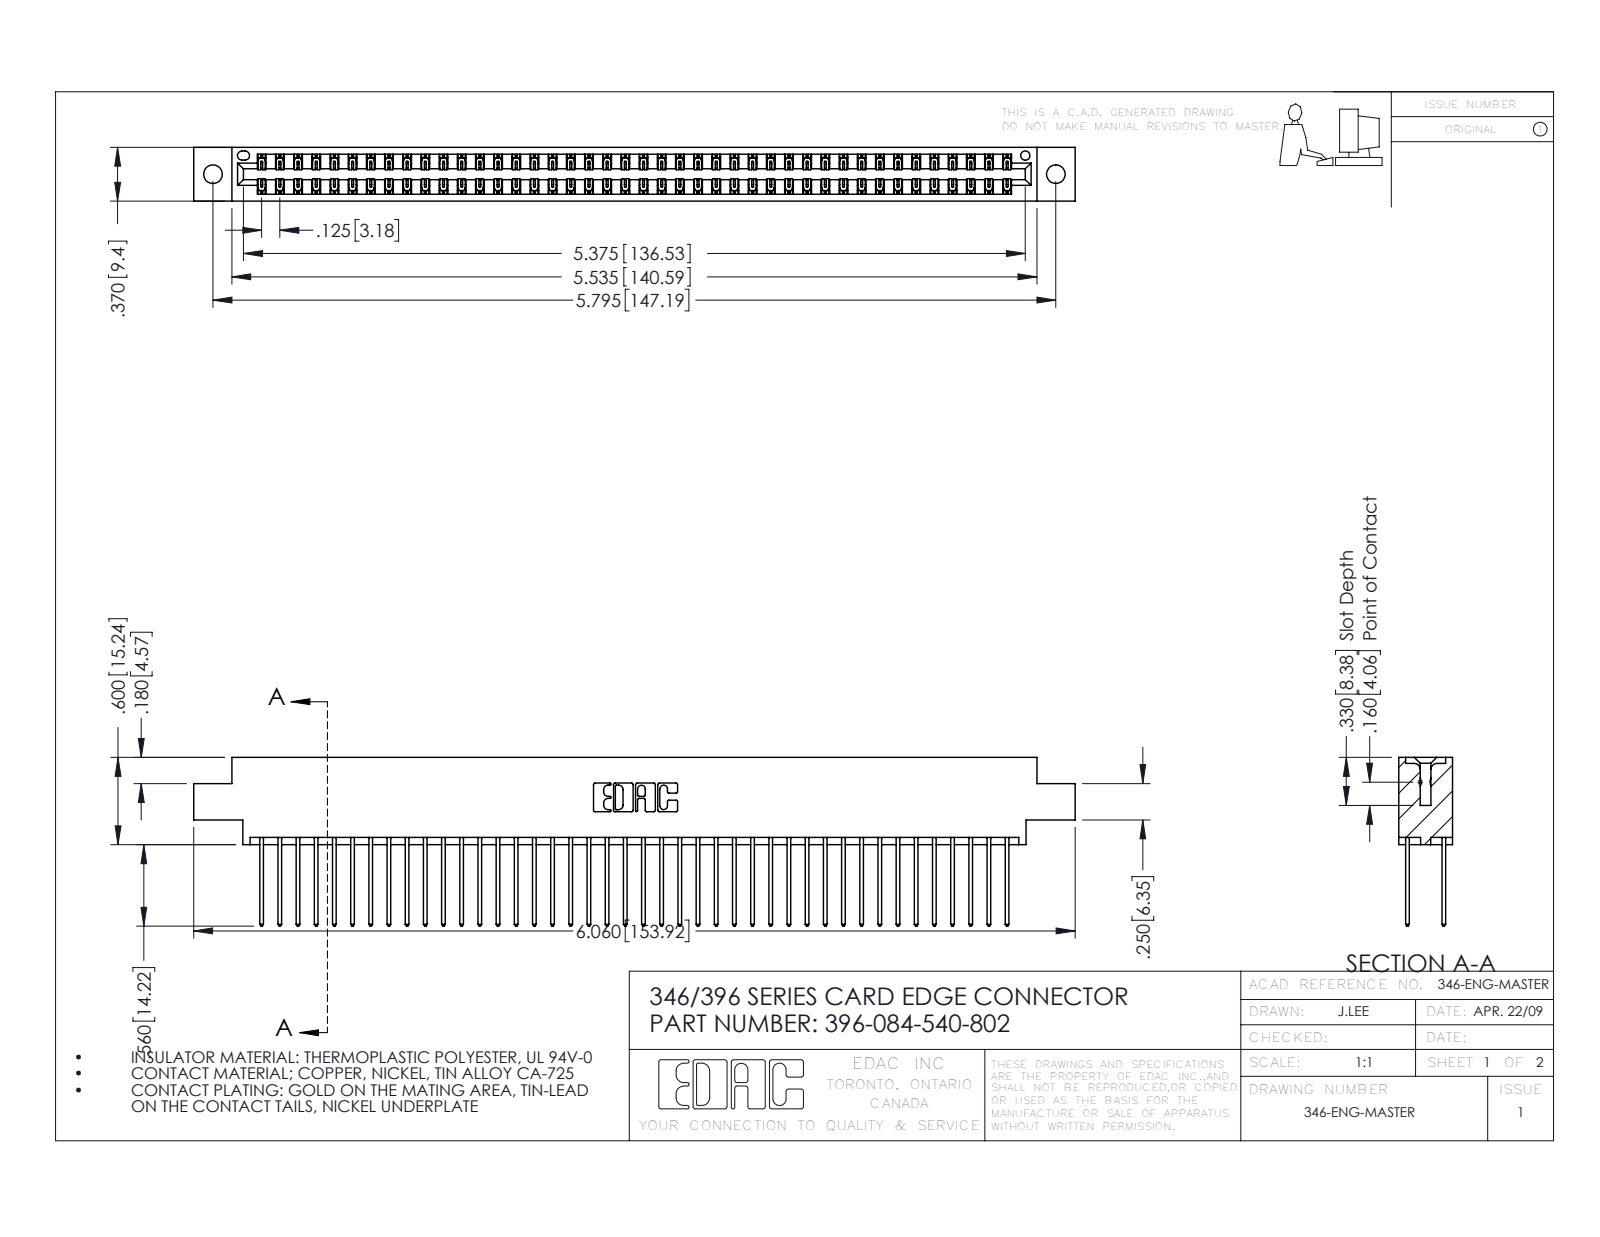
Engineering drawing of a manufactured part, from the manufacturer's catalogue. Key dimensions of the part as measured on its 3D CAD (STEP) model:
Part name (STEP PRODUCT): 396-084-540-802; 345-292-001_345-293-140; 346 Part_0.170 Offset - 0.128 Dia
STEP written by: SolidWorks 2016 (CONFIG_CONTROL_DESIGN)
Units: inches
Bodies: 85 solids, 4494 faces (3020 planar, 1474 cylindrical, 0 other)
Overall size (bounding box): 6.06 × 1.16 × 0.37
Volume: 0.924 in³ · Surface area: 34.45 in²
Round holes (diameter × count): ⌀0.128 ×2, ⌀0.064 ×1
Partial cylindrical surfaces — rounded edges, fillets, slot ends (radius × count): R0.006 ×126, R0.01 ×84, R0.01 ×22, R0.007 ×6, R0.031 ×6, R0.026 ×3, R0.014 ×2, R0.022 ×2
Main face-to-face distances: 0.048, 0.322, 0.25, 0.072, 0.298, 0.025, 0.37, 0.275, 0.148, 0.222
Hole centre spacings: 0.246, 5.586, 5.795
